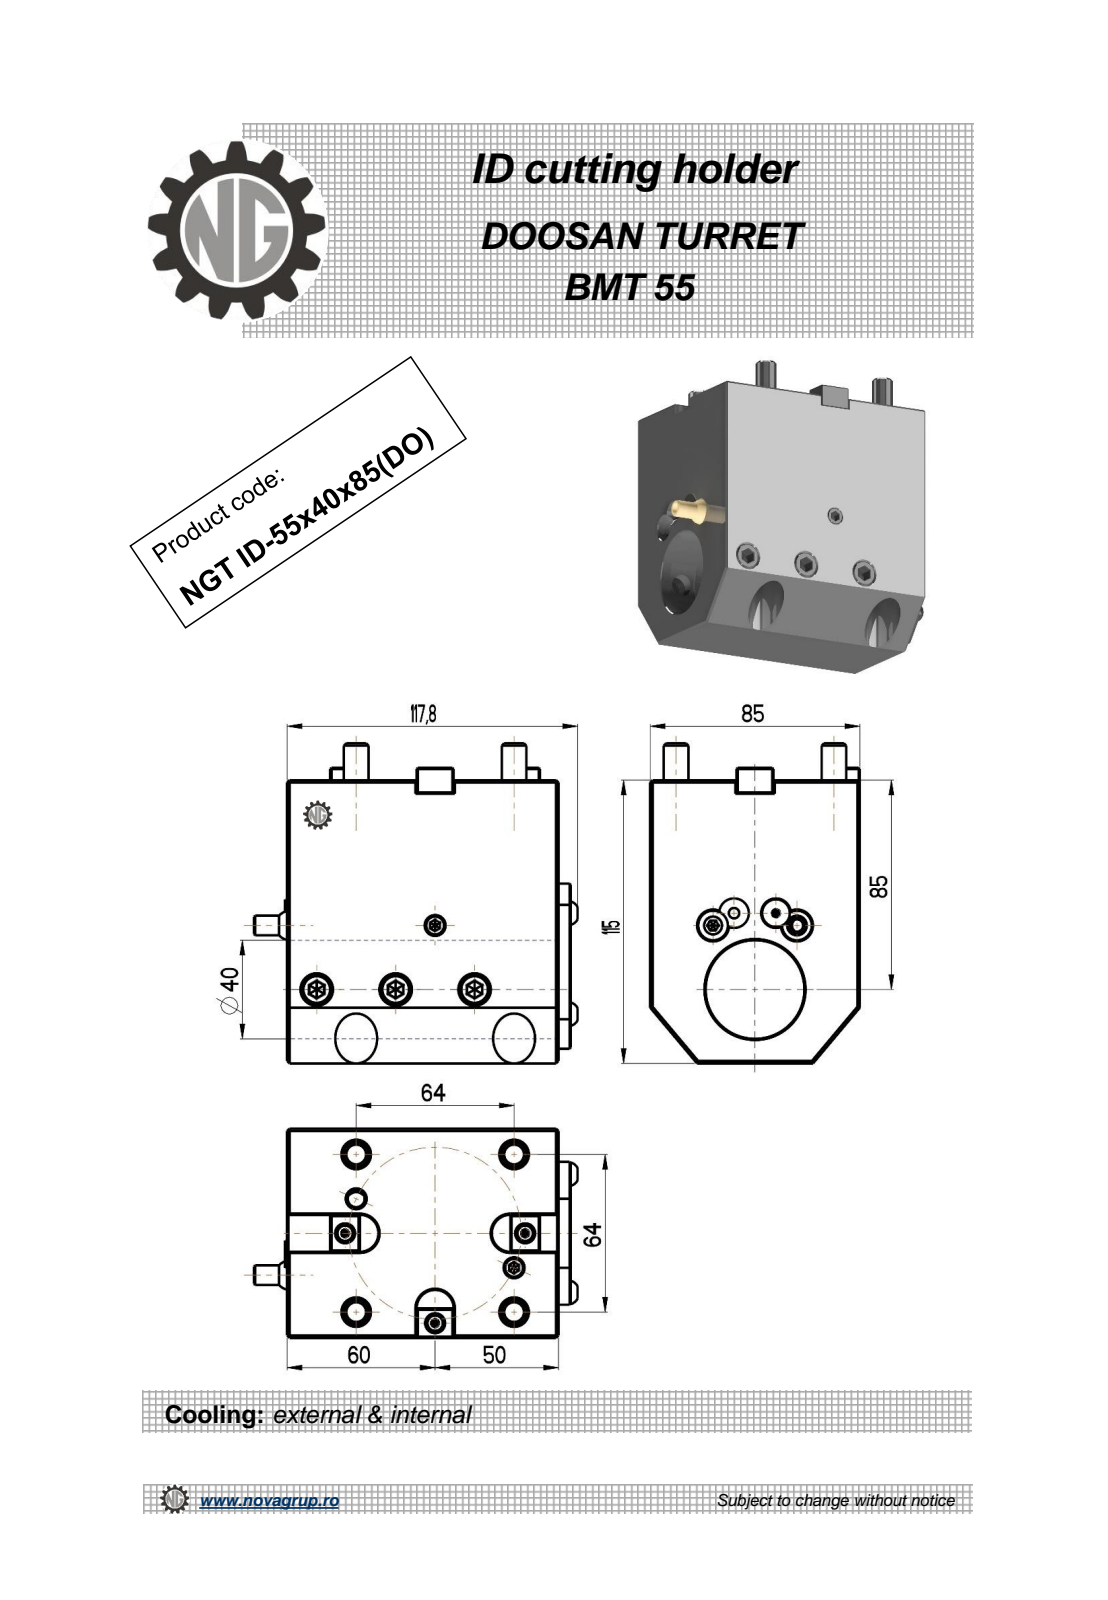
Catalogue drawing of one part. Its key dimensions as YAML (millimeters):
part_name: "NGT_ID_55_40_85_DO"
step_written_by: "PRO/ENGINEER BY PARAMETRIC TECHNOLOGY CORPORATION, 2010280 (CONFIG_CONTROL_DESIGN)"
units: millimeters
bodies: {solids: 1, faces: 390, planar: 212, cylindrical: 80, other: 98}
overall_size: [131.19, 130, 85]
volume: 905603
surface_area: 82267
round_holes:
  - {diameter: 10.2, count: 3}
  - {diameter: 5, count: 1}
  - {diameter: 6.8, count: 1}
  - {diameter: 40, count: 1}
round_bosses_or_shafts:
  - {diameter: 10, count: 4}
  - {diameter: 11.2, count: 1}
  - {diameter: 8, count: 1}
partial_cylinders:
  - {radius: 0.61, count: 36}
  - {radius: 0.22, count: 6}
  - {radius: 0.41, count: 6}
  - {radius: 7.5, count: 3}
face_to_face_distances: [85, 115, 110, 5, 16, 35, 10, 50, 73, 15]
hole_center_spacings: [32, 31.06, 64]
